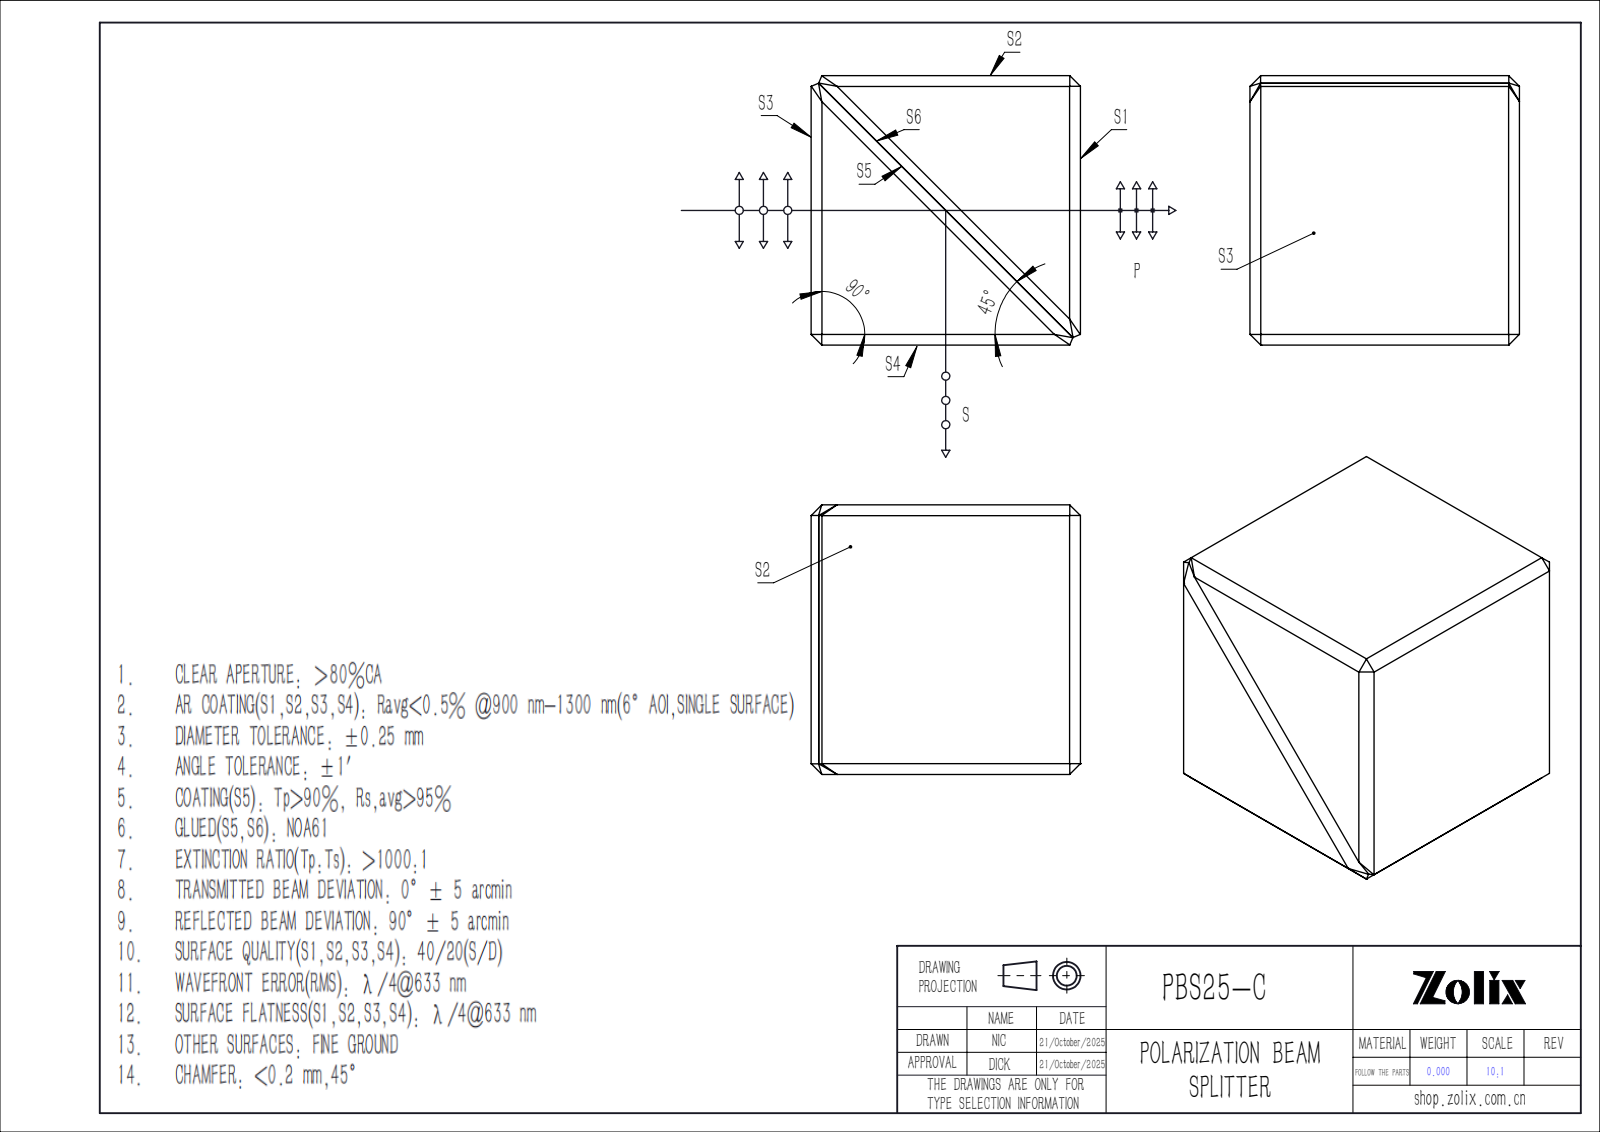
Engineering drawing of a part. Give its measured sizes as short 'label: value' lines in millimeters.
name: PBS643-1-1; PBS643; PBS643-1-2
written by: SolidWorks 2022 (CONFIG_CONTROL_DESIGN)
unit: mm
bodies: 2 solids, 43 faces (41 planar, 2 cylindrical, 0 other)
size: 25.4 × 25.4 × 25.4
volume: 16 378 mm³; area: 5 624 mm²
holes: 1× ⌀0.5
face distances: 25.4, 35.63, 17.67, 35.64, 32.83, 17.81, 17.82, 43.51, 38.13, 38.14
